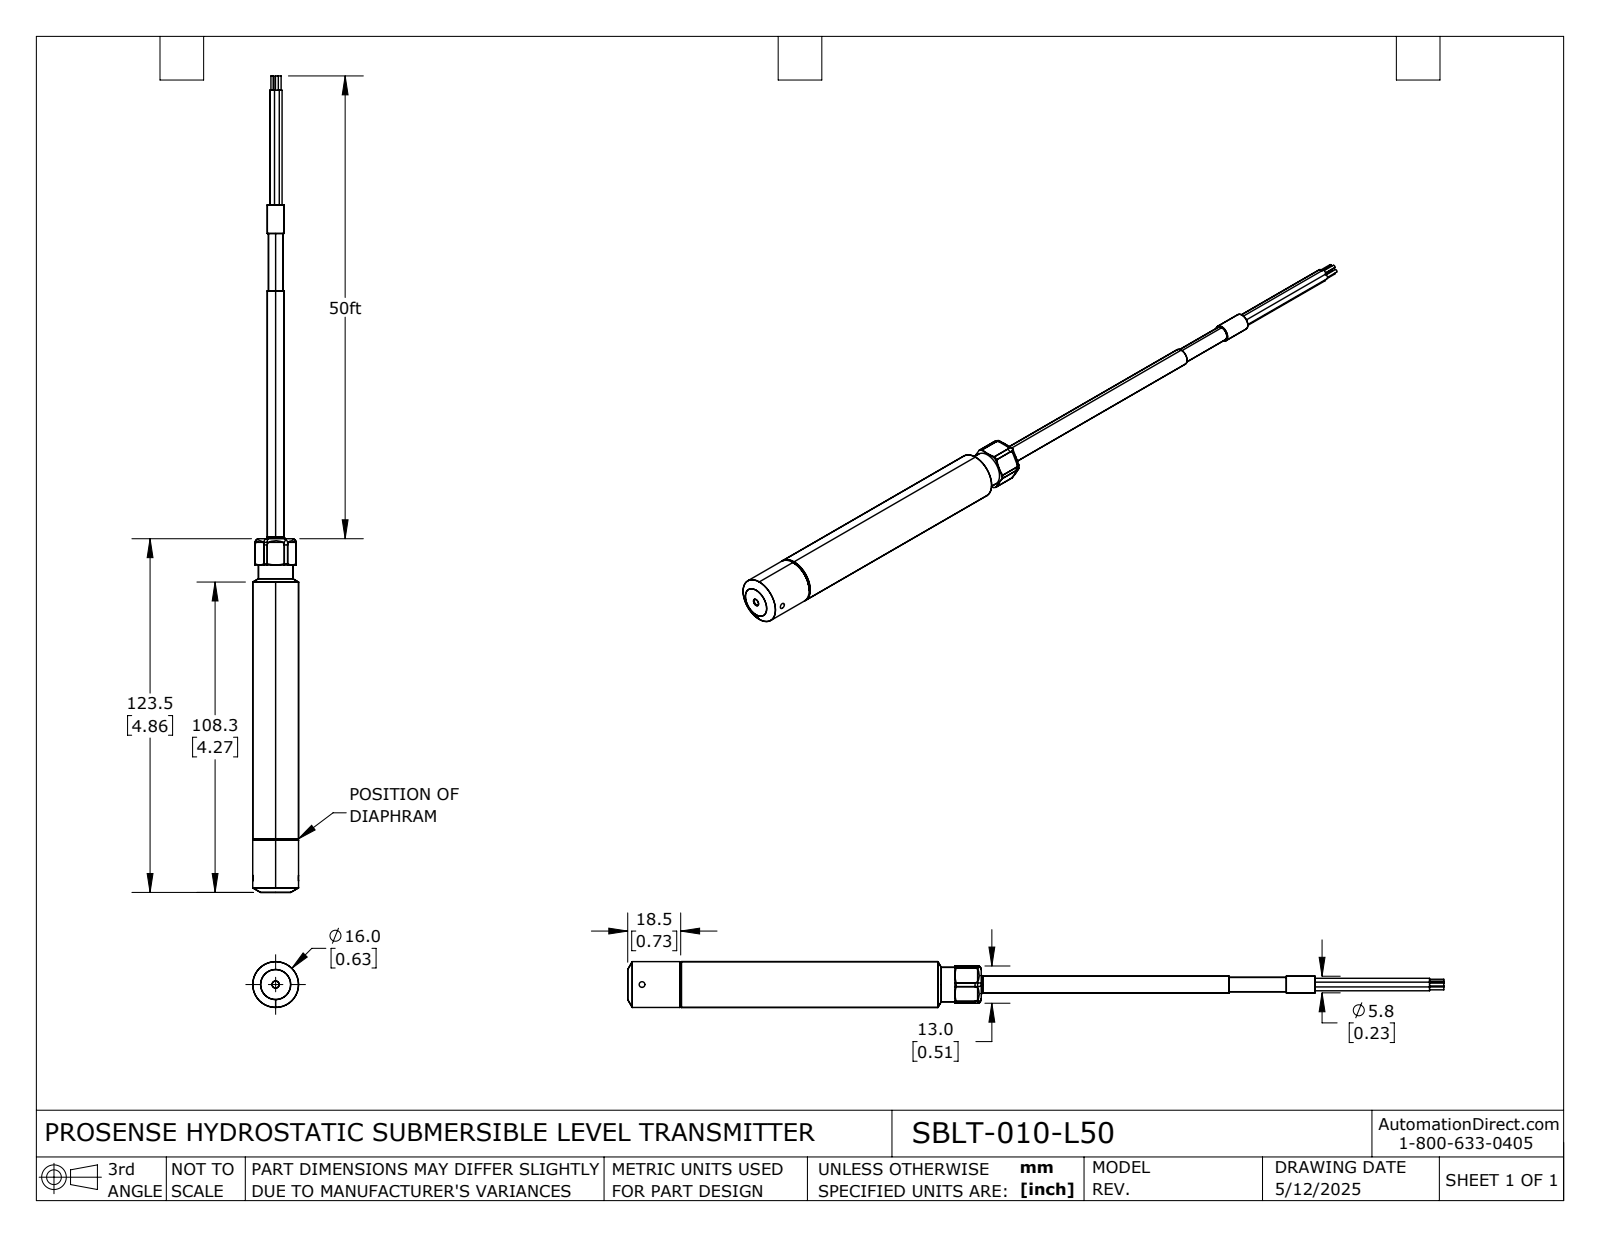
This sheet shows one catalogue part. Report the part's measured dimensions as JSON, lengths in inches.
{"part_name": "SBLT-010-L50", "step_written_by": "SolidWorks 2024 (AUTOMOTIVE_DESIGN)", "units": "inches", "bodies": {"solids": 11, "faces": 201, "planar": 52, "cylindrical": 88, "other": 61}, "overall_size": [11.221, 0.63, 0.63], "volume_in3": 3.198, "surface_area_in2": 29.94, "round_holes": [[0.079, 1], [0.098, 1], [0.374, 1], [0.516, 1], [0.551, 1]], "round_bosses_or_shafts": [[0.066, 5], [0.039, 5], [0.63, 1], [0.629, 1], [0.472, 1], [0.472, 1], [0.244, 1], [0.228, 1]], "partial_cylinders_radius": [[0.05, 6], [0.281, 1]], "face_to_face_distances": [0.512, 4.861, 4.33, 0.531, 4.589, 8.918, 9.45, 3.77, 0.197, 8.721]}
